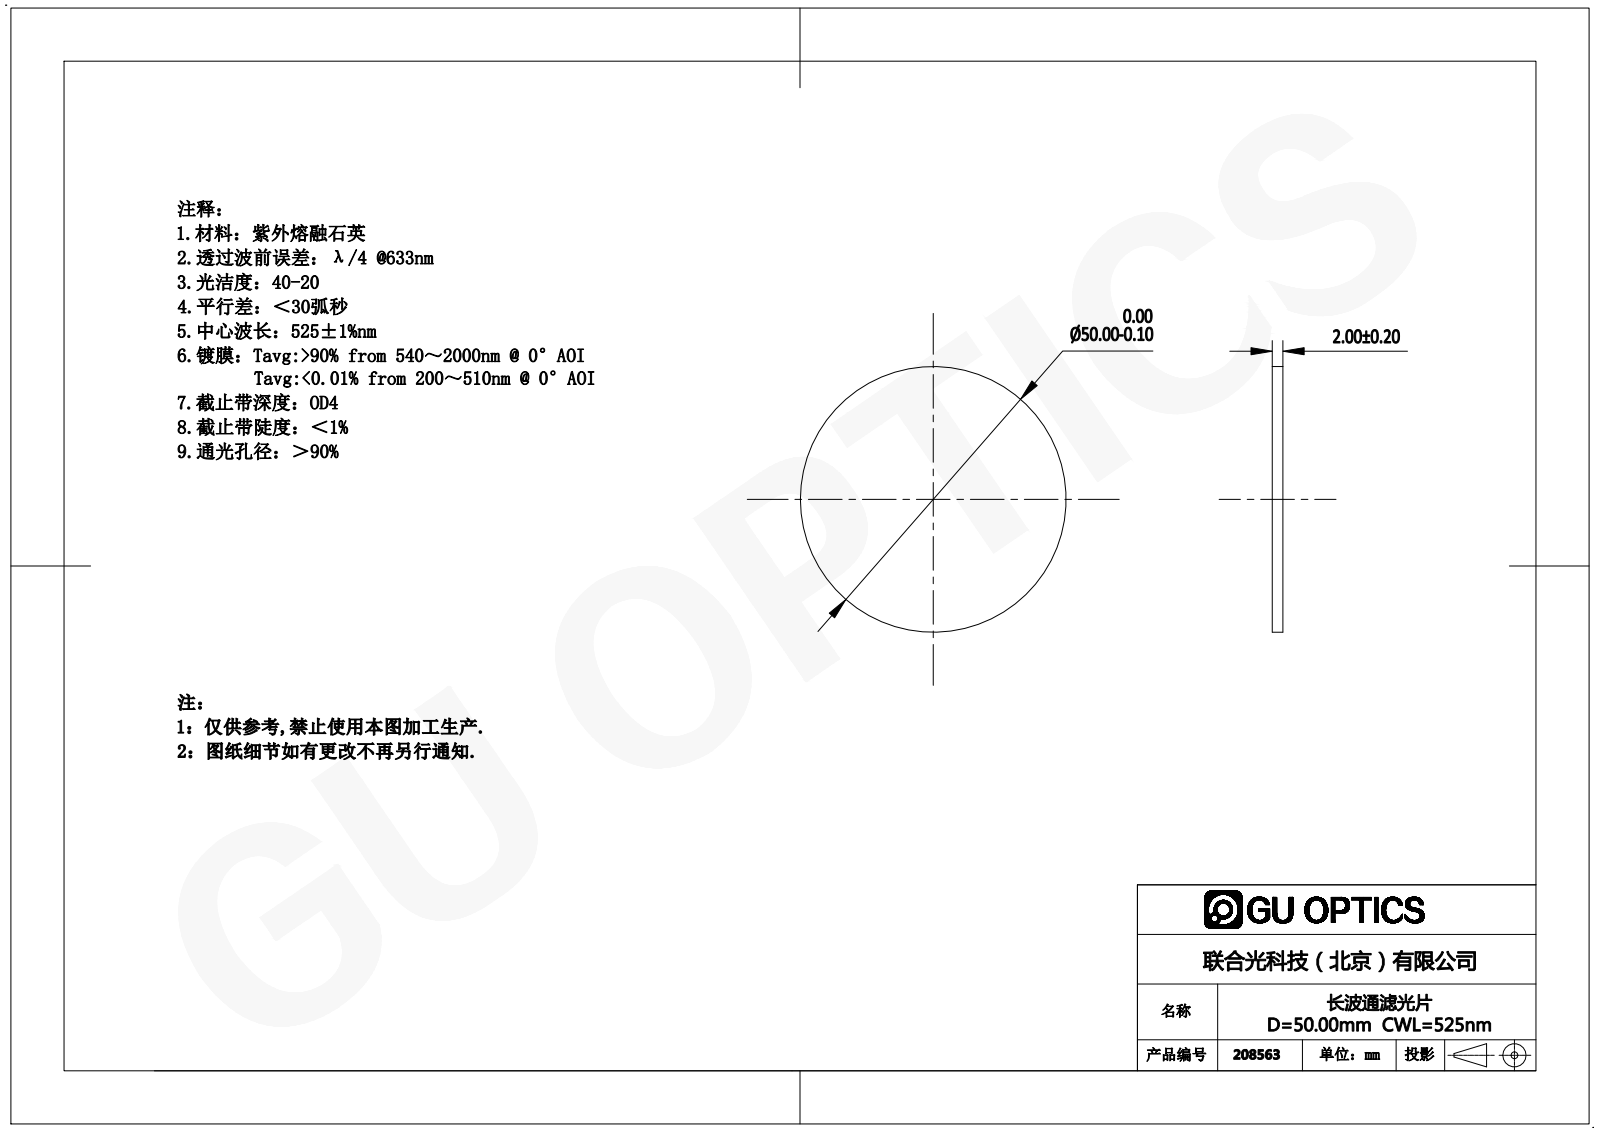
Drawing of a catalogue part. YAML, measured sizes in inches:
part_name: "208558"
step_written_by: "SolidWorks 2016 (AUTOMOTIVE_DESIGN)"
units: inches
bodies: {solids: 1, faces: 4, planar: 2, cylindrical: 2, other: 0}
overall_size: [1.969, 1.969, 0.079]
volume: 0.24
surface_area: 6.574
round_bosses_or_shafts:
  - {diameter: 1.969, count: 1}
face_to_face_distances: [0.079]
